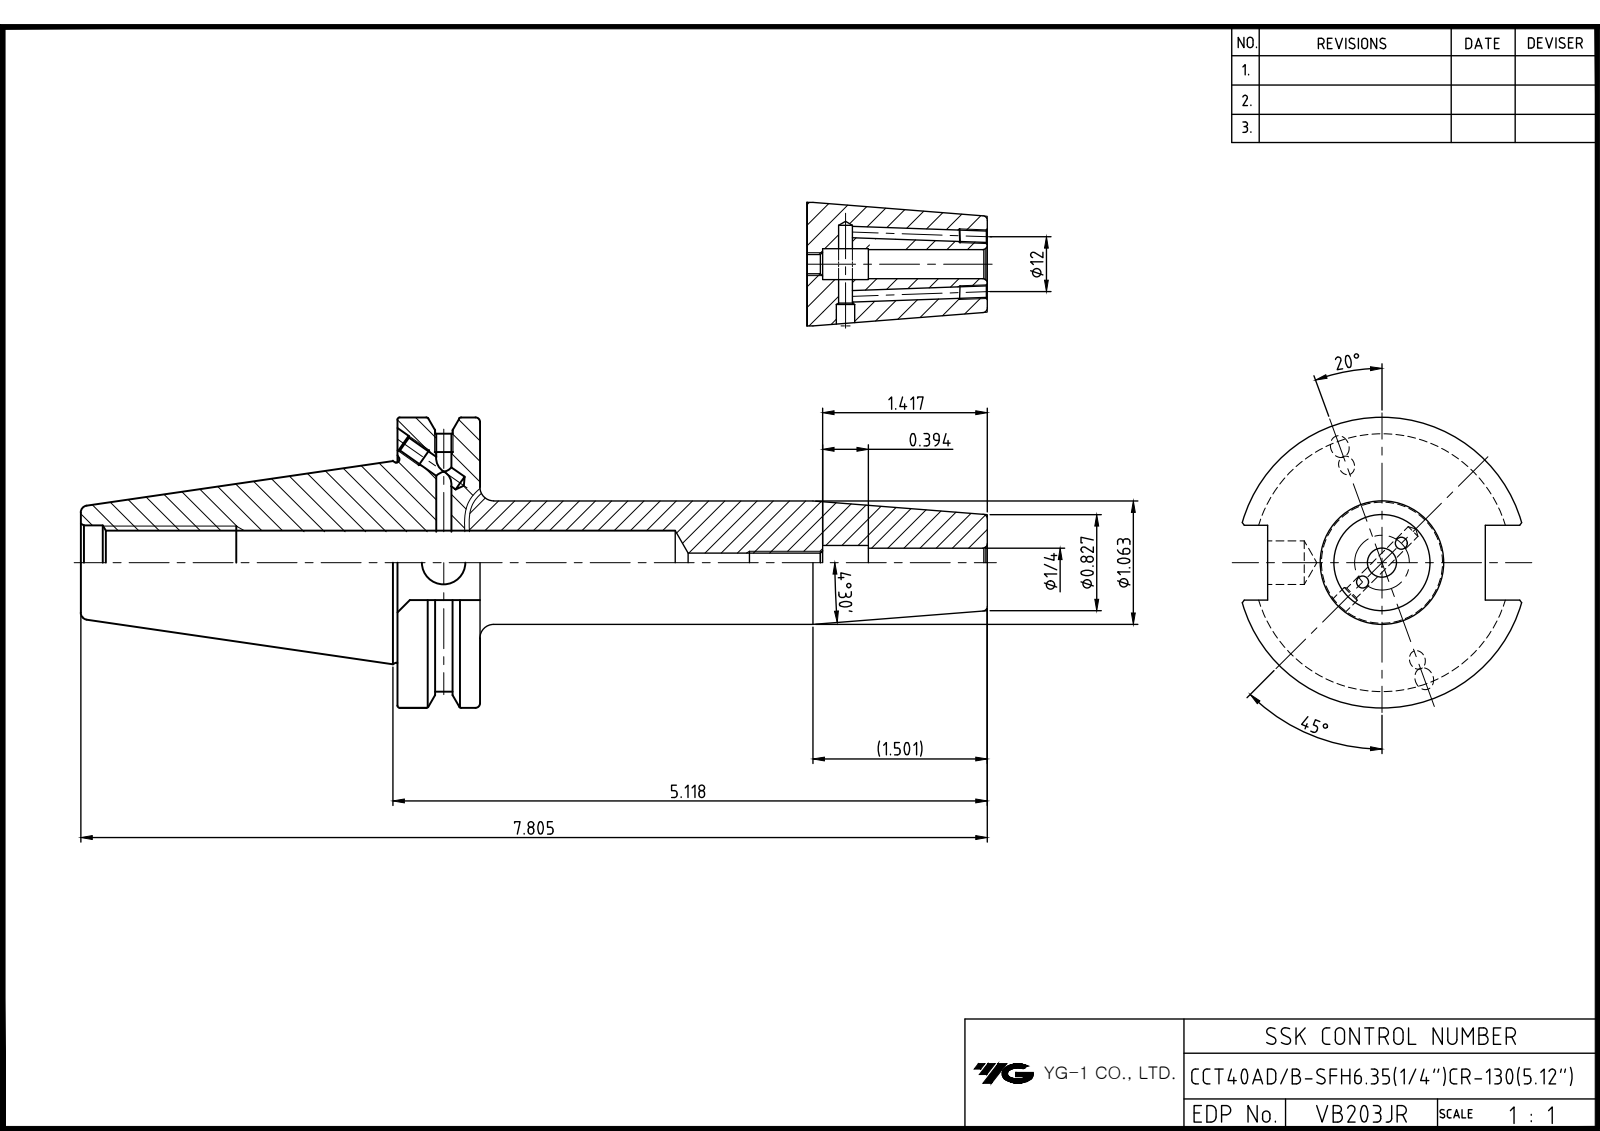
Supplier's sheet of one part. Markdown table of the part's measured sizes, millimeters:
| quantity | value |
| --- | --- |
| part name | LO-CCT40ADB-6.35CR-130 |
| STEP written by | Autodesk Inventor 2026 (AUTOMOTIVE_DESIGN) |
| units | millimeters |
| bodies | 1 solid, 91 faces (38 planar, 30 cylindrical, 23 other) |
| overall size | 198.25 × 63.5 × 61.09 |
| volume | 154 400 mm³ |
| surface area | 33 418 mm² |
| round holes (diameter × count) | 3.24 × 4, 2.46 × 2, 4 × 2, 4.2 × 2, 4.3 × 1, 6.35 × 1, 7.55 × 1, 9.53 × 1, 13.39 × 1, 16.3 × 1 |
| round bosses / shafts (diameter × count) | 63.5 × 1, 43.8 × 1, 27 × 1 |
| partial cylindrical surfaces (radius × count) | 28.15 × 1 |
| main face-to-face distances | 18.05, 129, 110.95, 47.6, 16.38, 69.25, 87.3, 198.25, 81.34, 12.09 |
